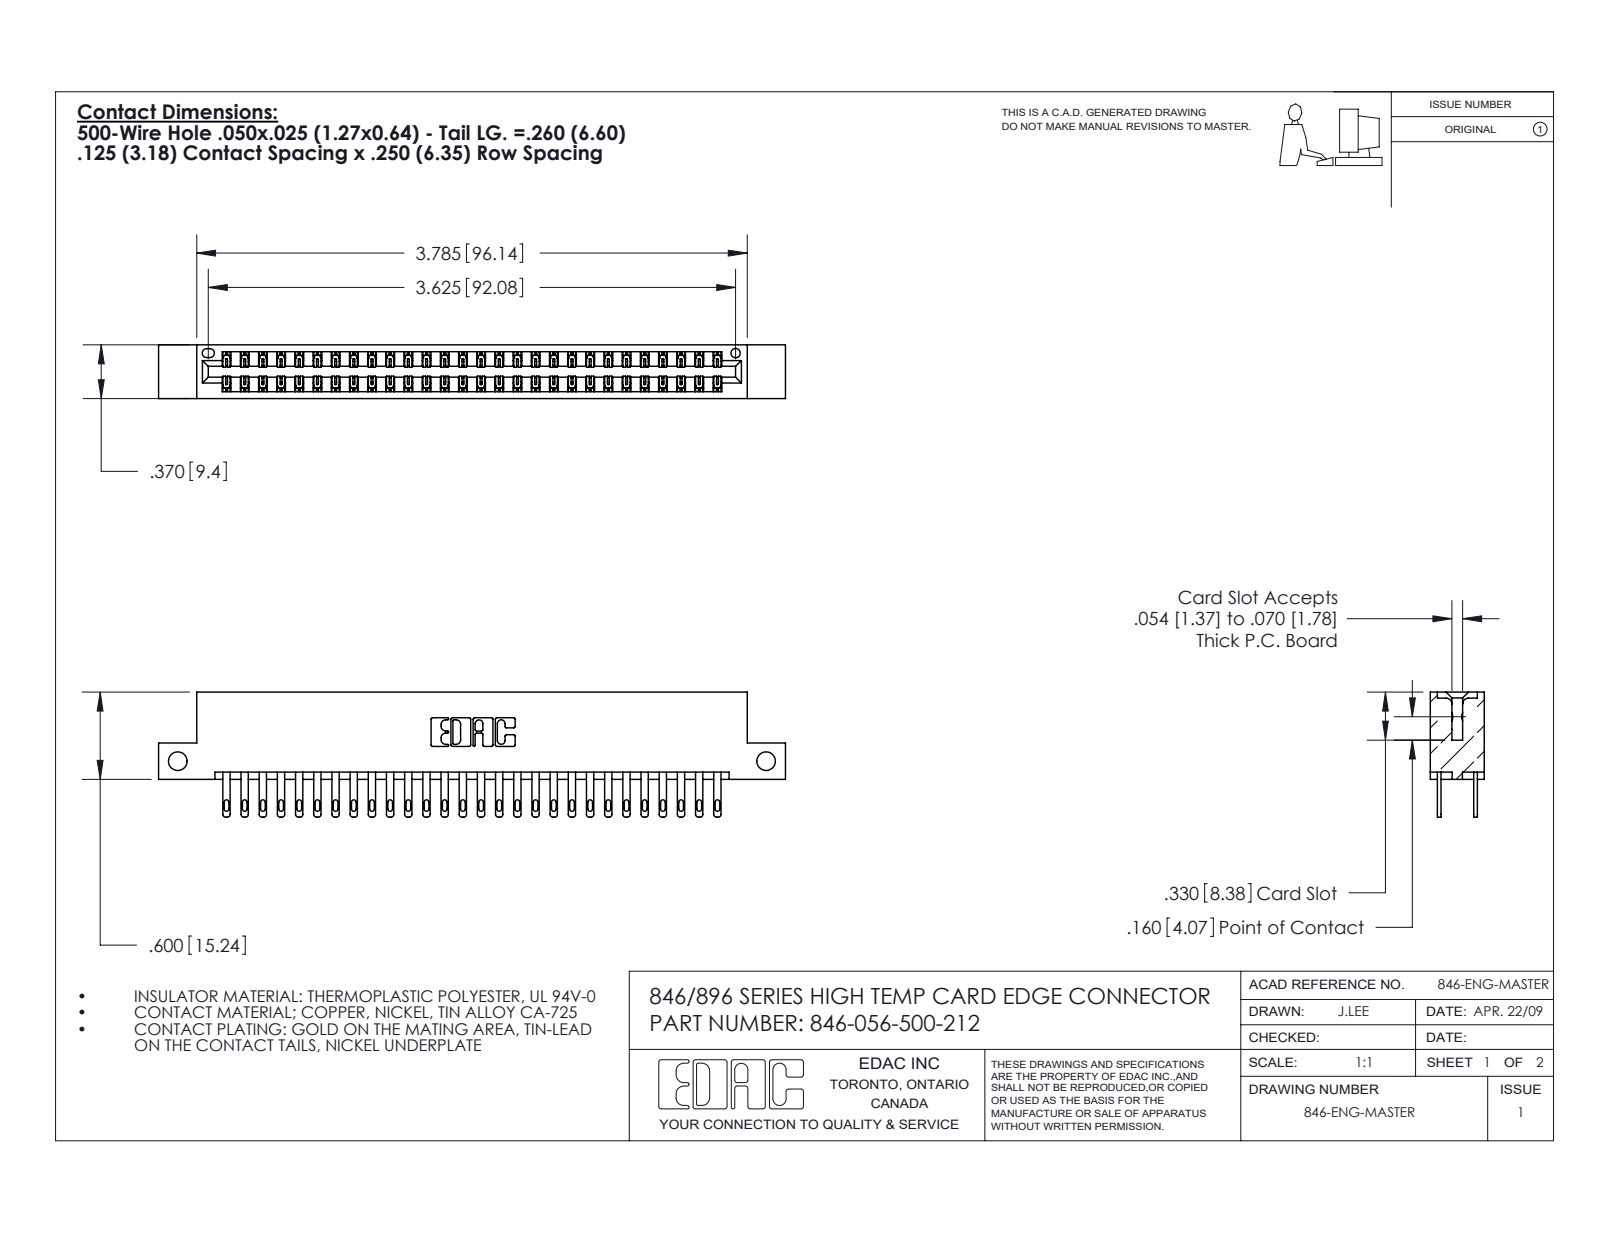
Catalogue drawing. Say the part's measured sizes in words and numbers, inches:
The part is named "345-292-001_345-293-100; 346 Part_Flush Mounting Lugs - Side Mount; 346-056-500-212". Its 3-D file was written by "SolidWorks 2016 (CONFIG_CONTROL_DESIGN)". It is 57 solids with 2810 faces: 1700 planar, 1110 cylindrical and 0 other. Overall it measures 4.31 by 0.86 by 0.37 inches. Its volume is 0.65 cubic inches and its surface area 23.05 square inches. Round holes: 2 of diameter 0.128, 1 of diameter 0.064. Partial cylindrical surfaces (rounded edges, fillets, slot ends): 84 of radius 0.006, 56 of radius 0.016, 56 of radius 0.02, 22 of radius 0.01, 6 of radius 0.007, 6 of radius 0.031, 3 of radius 0.026, 2 of radius 0.014. The main face-to-face distances are 0.048, 0.322, 0.25, 0.072, 0.298, 0.025, 0.37, 0.275, 0.148, 0.222. The hole center spacings are 4.045.
